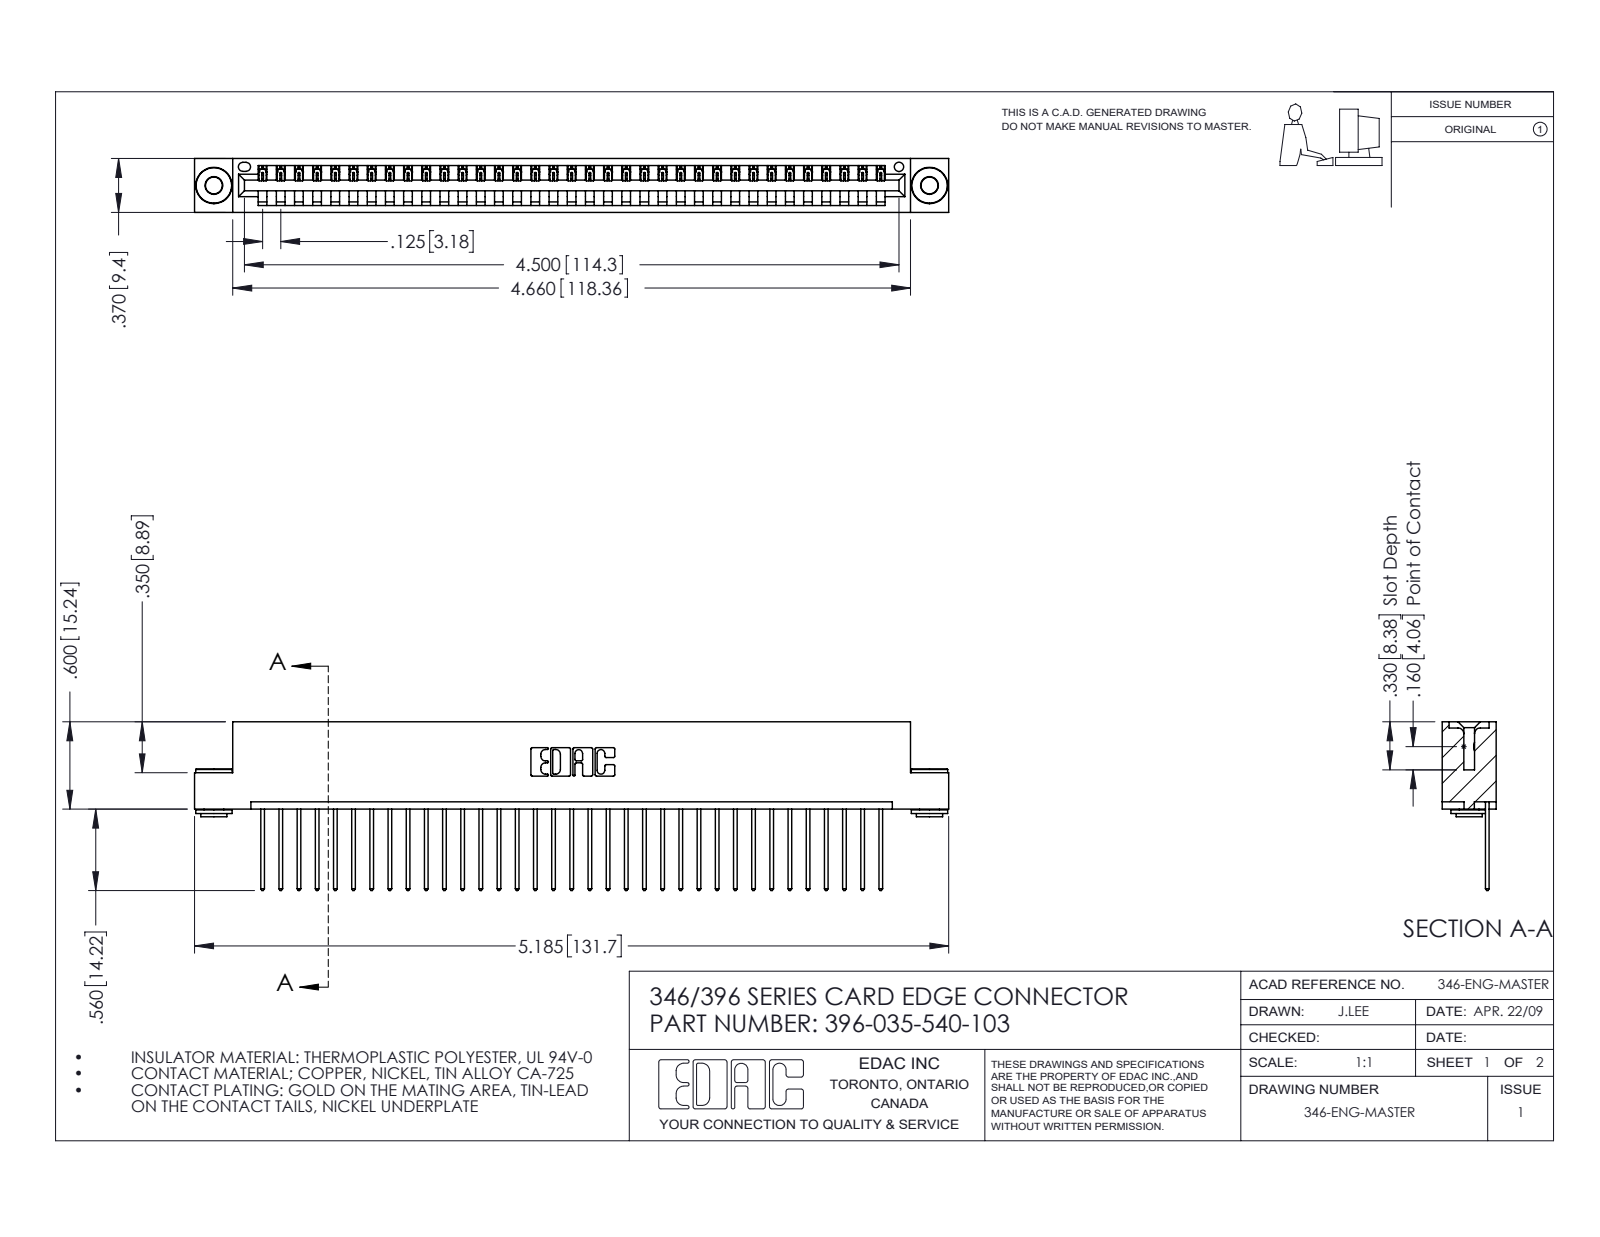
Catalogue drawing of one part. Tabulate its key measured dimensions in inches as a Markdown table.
| quantity | value |
| --- | --- |
| part name | 345-250-002_345-250-002-102; 345-292-001_345-293-140; 346 Part_Flush Mounting Lugs - 0.156 Dia-TH; 396-035-540-103 |
| STEP written by | SolidWorks 2016 (CONFIG_CONTROL_DESIGN) |
| units | inches |
| bodies | 38 solids, 2190 faces (1486 planar, 696 cylindrical, 8 other) |
| overall size | 5.185 × 1.16 × 0.37 |
| volume | 0.77 in³ |
| surface area | 25.22 in² |
| round holes (diameter × count) | 0.116 × 2, 0.156 × 2, 0.064 × 1 |
| round bosses / shafts (diameter × count) | 0.25 × 2, 0.18 × 2, 0.136 × 2 |
| partial cylindrical surfaces (radius × count) | 0.006 × 70, 0.01 × 70, 0.01 × 22, 0.007 × 6, 0.031 × 6, 0.026 × 3, 0.031 × 2, 0.04 × 2 |
| main face-to-face distances | 0.048, 0.322, 0.37, 0.25, 0.025, 0.072, 0.298, 0.148, 0.222, 0.1 |
| hole center spacings | 0.246, 4.711, 4.92 |
